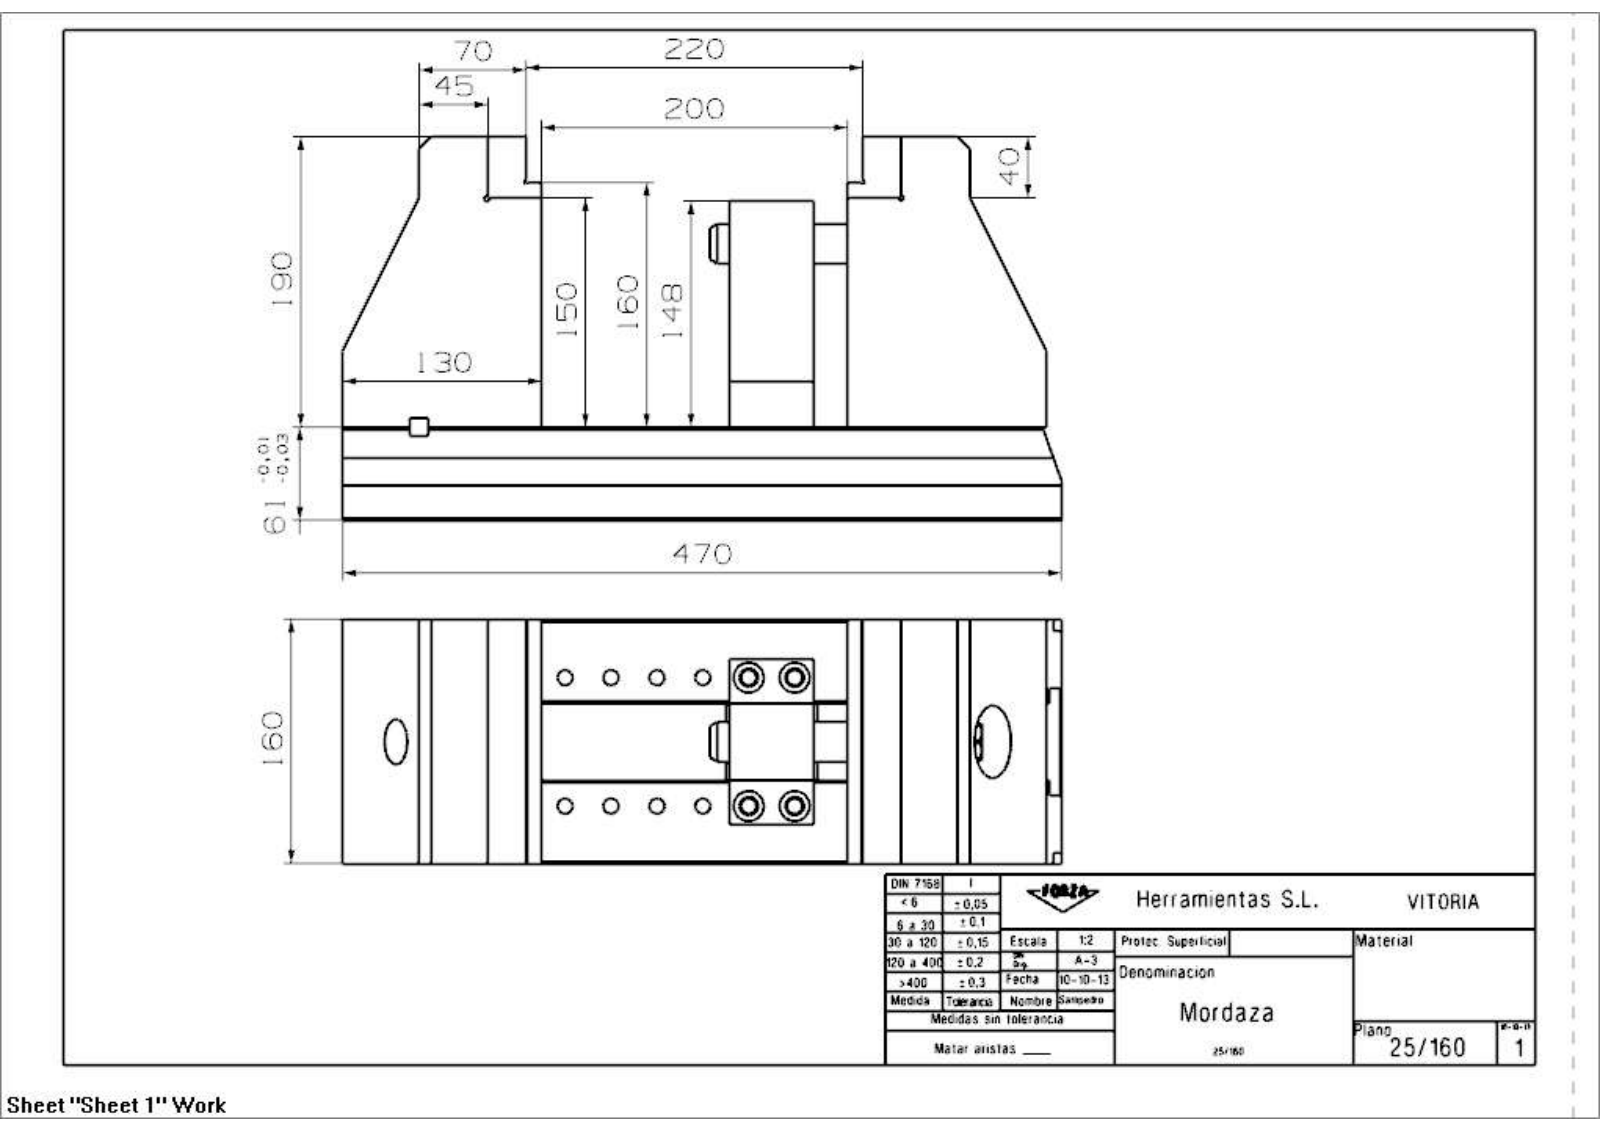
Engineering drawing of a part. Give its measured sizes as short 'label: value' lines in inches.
name: 25_160_Mordaza
written by: SIEMENS PLM Software NX 7.5 (AUTOMOTIVE_DESIGN)
unit: in
bodies: 18 solids, 382 faces (205 planar, 116 cylindrical, 61 other)
size: 18.504 × 9.882 × 6.299
volume: 565.7 in³; area: 1 246 in²
holes: 20× ⌀0.404, 14× ⌀0.492, 8× ⌀0.748, 6× ⌀0.472, 6× ⌀0.591, 6× ⌀0.866, 4× ⌀0.413, 4× ⌀0.787, 2× ⌀0.906, 1× ⌀0.204, 1× ⌀0.394, 1× ⌀0.837
bosses: 1× ⌀1.732, 1× ⌀1.654, 1× ⌀1.331, 1× ⌀0.906, 1× ⌀0.803
rounds: 4× R0.016, 2× R0.256, 1× R0.522
face distances: 6.299, 2.402, 1.15, 1.252, 0.394, 4.016, 1.772, 0.276, 0.984, 1.969
hole spacings: 1.181, 3.512, 2.362, 4.064, 3.543, 4.847, 3.307, 4.724
